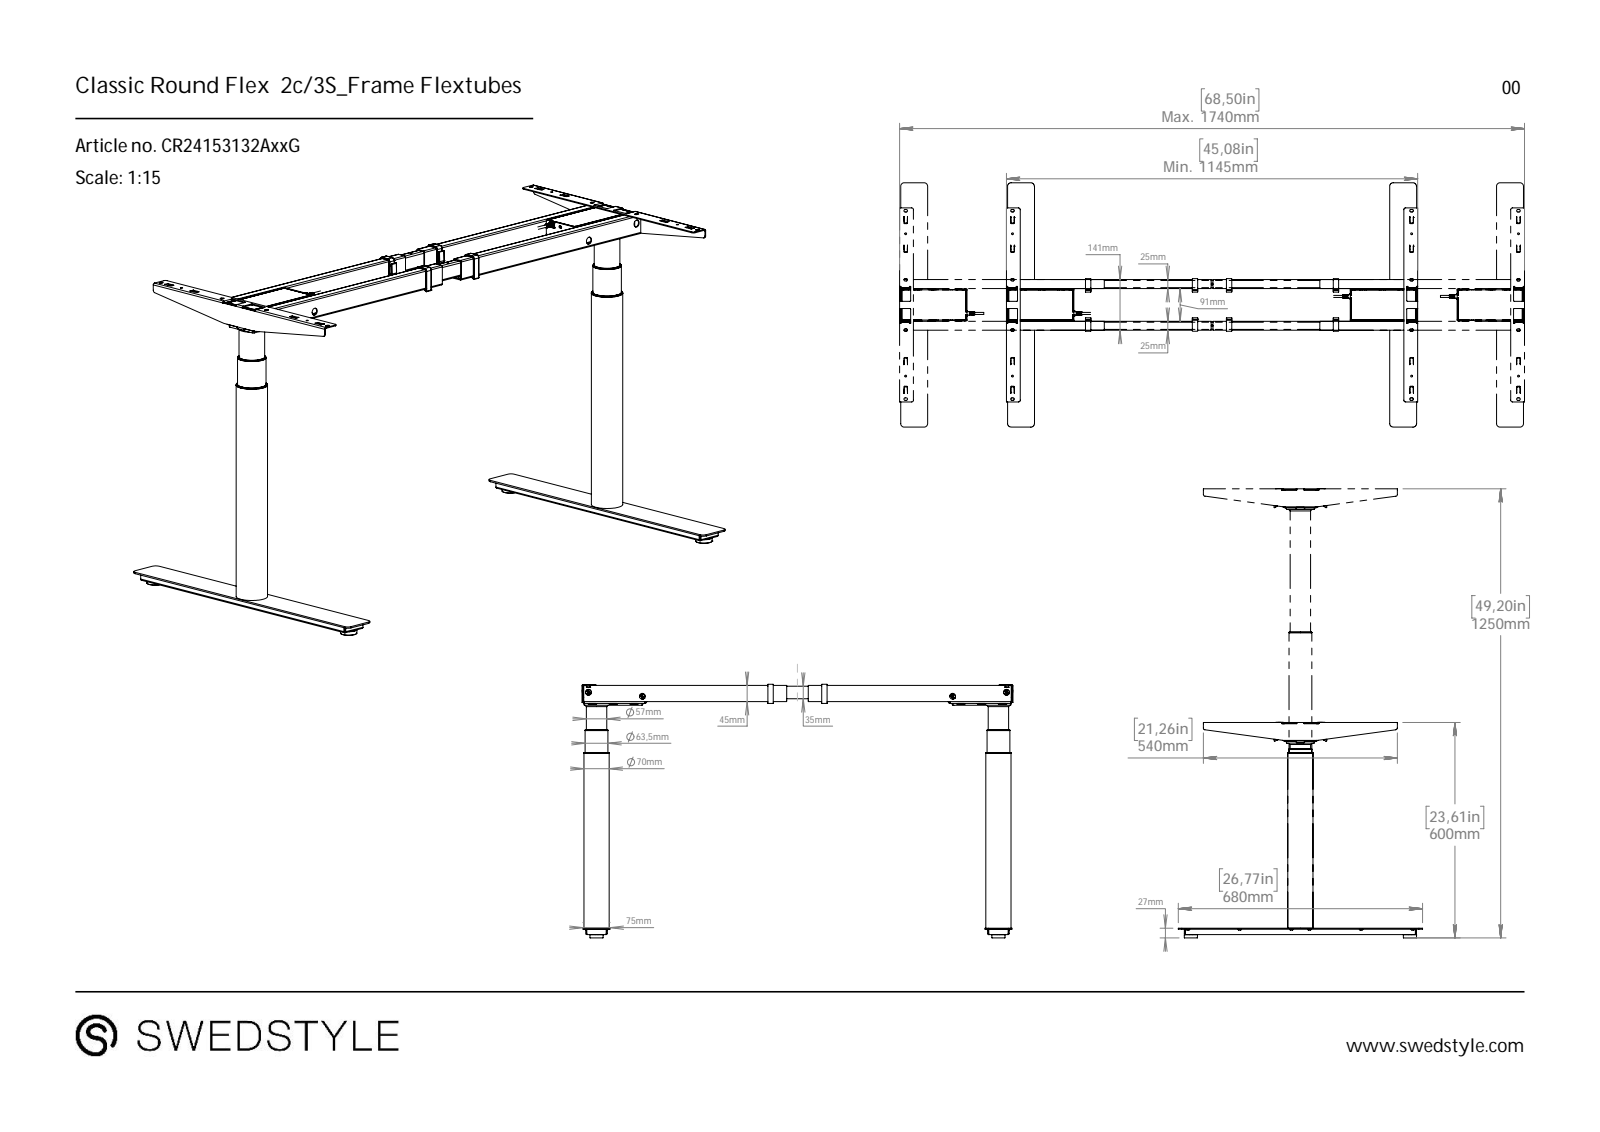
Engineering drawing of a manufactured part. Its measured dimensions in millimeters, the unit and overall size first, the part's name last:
Units: millimetres
Overall size (bounding box): 1200 × 705.7 × 680
Round holes (diameter × count): ⌀15 ×8, ⌀5 ×4, ⌀16 ×4, ⌀4.2 ×2, ⌀6 ×2, ⌀5.4 ×1
Round bosses / shafts (diameter × count): ⌀70 ×2, ⌀63.5 ×2, ⌀57 ×2, ⌀8.5 ×2, ⌀5.5 ×2
Partial cylindrical surfaces — rounded edges, fillets, slot ends (radius × count): R0.5 ×92, R3 ×65, R2.5 ×56, R3.5 ×28, R1 ×15, R10 ×8, R1.5 ×6, R5 ×6
Main face-to-face distances: 2, 116, 3, 23, 2.5, 0.5, 93, 22.5, 20.5, 15
Hole centre spacings: 22, 34, 40.5, 95.52, 117.24, 181.43, 184.26, 215.36
Bodies: 0 solids, 1431 faces (624 planar, 485 cylindrical, 322 other)
Part name (STEP PRODUCT): CR24153132AxxG_Classic Round Flex 2c_3S, Frame Flextubes Fl1145
STEP written by: SolidWorks 2021 (CONFIG_CONTROL_DESIGN)
